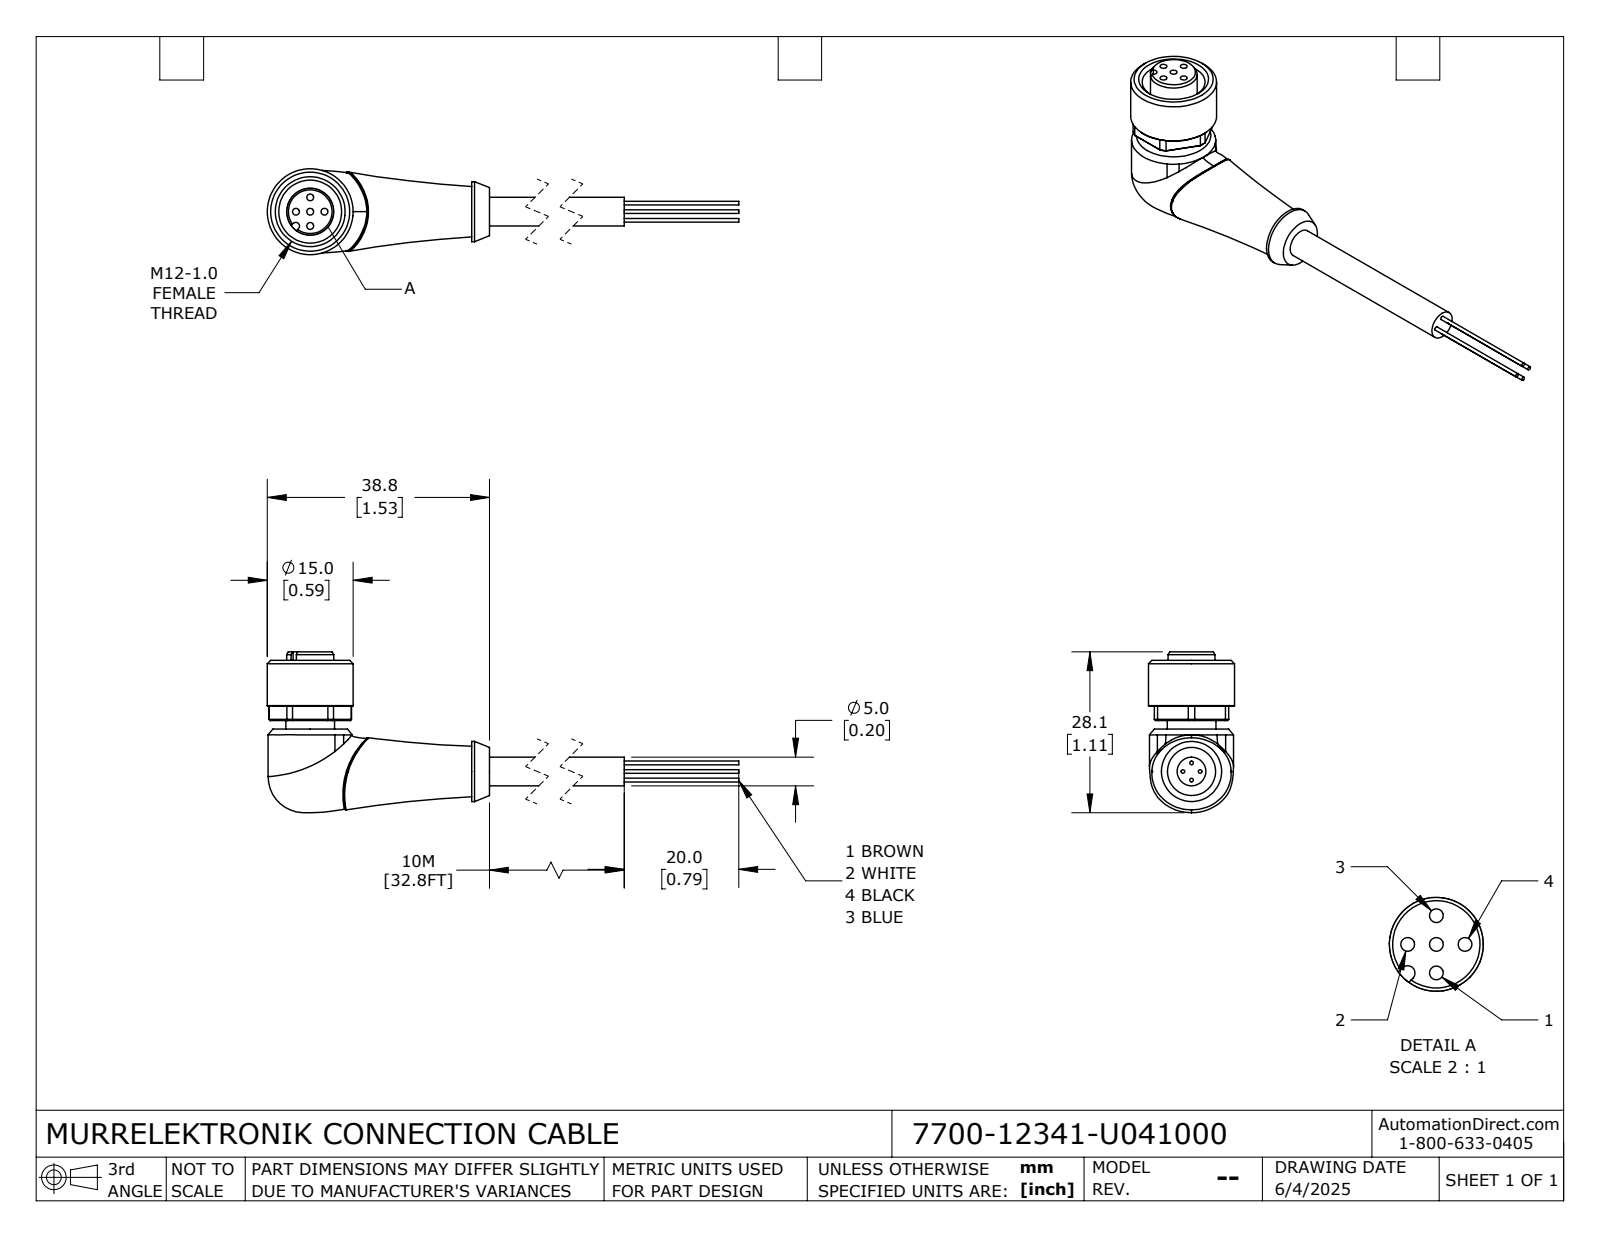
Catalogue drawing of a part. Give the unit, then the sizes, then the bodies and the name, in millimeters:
Units: millimetres
Overall size (bounding box): 93.8 × 28.11 × 15
Round holes (diameter × count): ⌀1.2 ×5, ⌀11 ×1
Round bosses / shafts (diameter × count): ⌀0.64 ×4, ⌀15 ×1, ⌀10.5 ×1, ⌀8.5 ×1, ⌀8.2 ×1, ⌀5 ×1
Partial cylindrical surfaces — rounded edges, fillets, slot ends (radius × count): R0.65 ×1, R7.2 ×1
Main face-to-face distances: 1.5, 12, 13, 4.5, 3, 13.5, 9, 10.5, 7.5, 2.5
Hole centre spacings: 2.5, 3.54, 5
Volume: 6 692 mm³ · Surface area: 3 745 mm²
Bodies: 1 solid, 109 faces (33 planar, 39 cylindrical, 37 other)
Part name (STEP PRODUCT): 7700-12341-U041000
STEP written by: SolidWorks 2024 (CONFIG_CONTROL_DESIGN)
